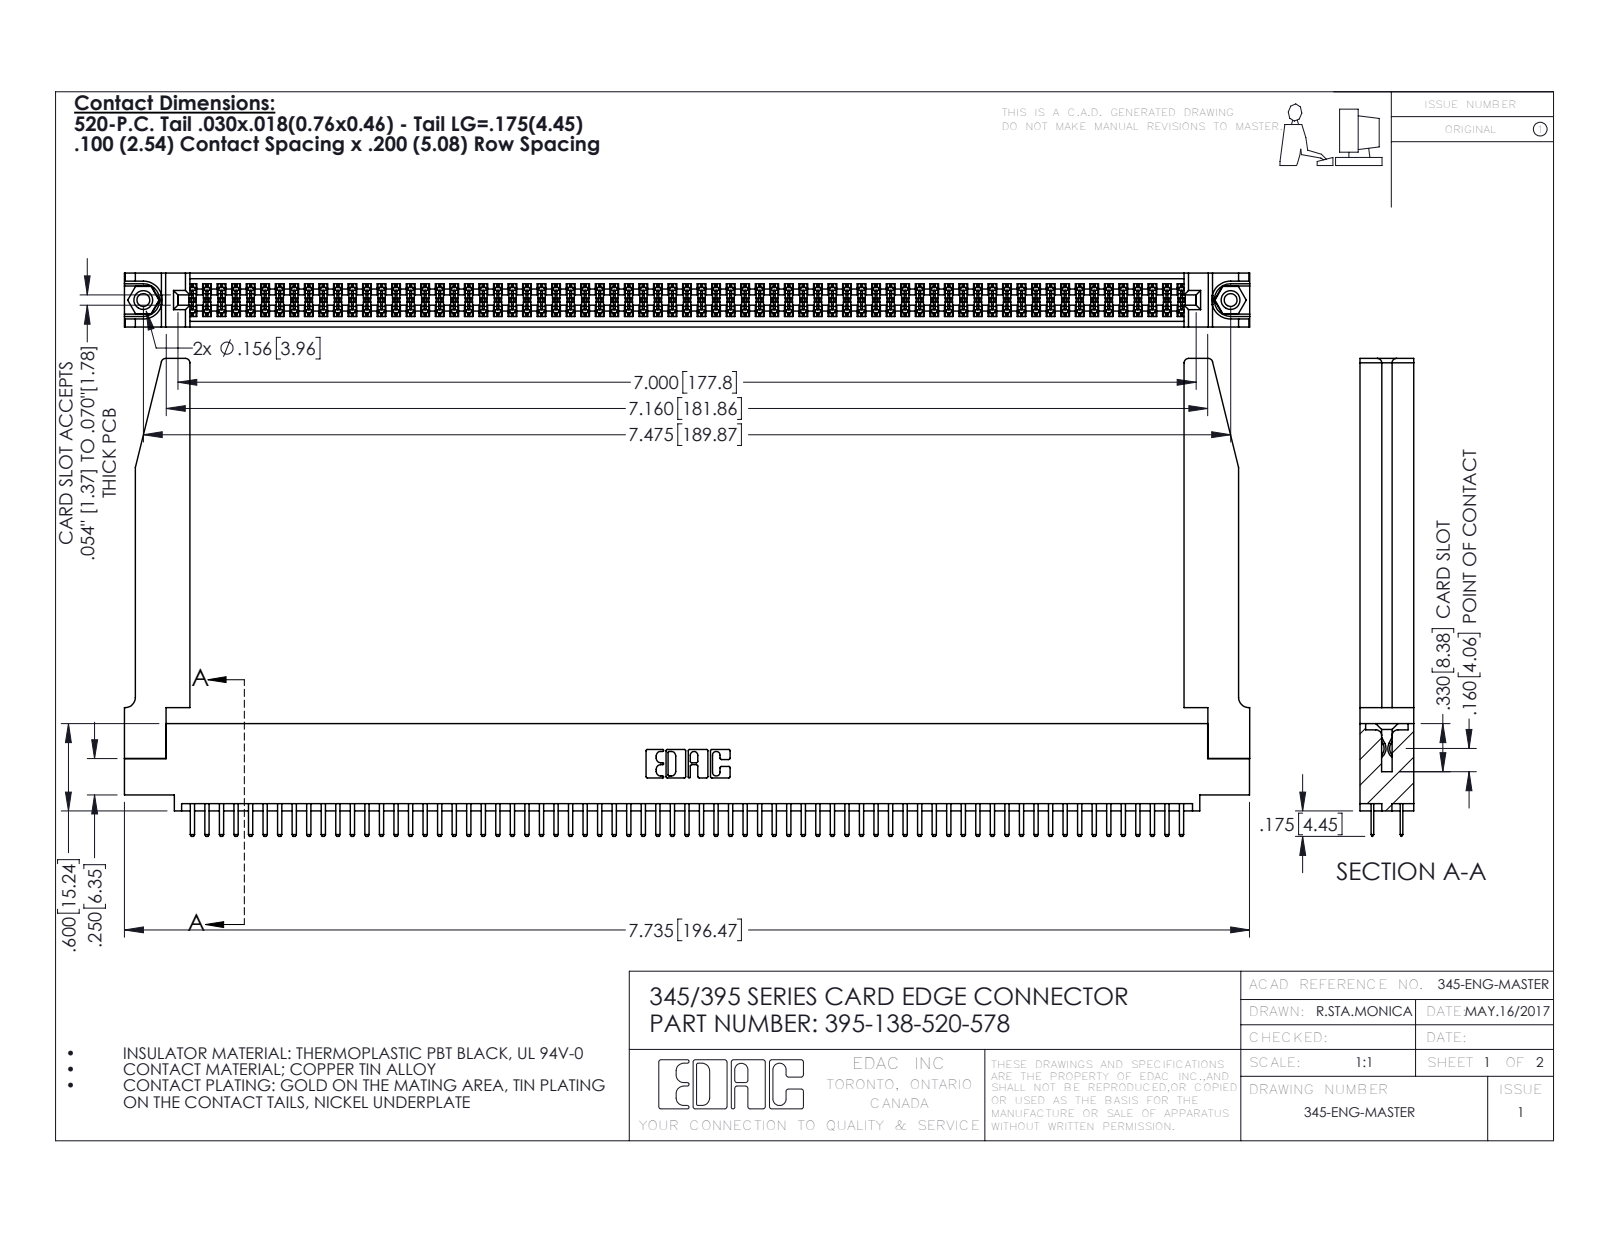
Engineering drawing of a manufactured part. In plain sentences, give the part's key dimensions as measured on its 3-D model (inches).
The part is named "345-250-001_345-250-001-102; 345-220-078_345-220-078; 345-292-001_345-293-120; 395-138-520-578 (+1 more)". Its 3-D file was written by "SolidWorks 2016 (CONFIG_CONTROL_DESIGN)". It is 143 solids with 7816 faces: 5056 planar, 2708 cylindrical and 52 other. Overall it measures 7.736 by 3.285 by 0.37 inches. Its volume is 1.646 cubic inches and its surface area 55.35 square inches. Round holes: 2 of diameter 0.089, 2 of diameter 0.125, 2 of diameter 0.156, 1 of diameter 0.064. Round bosses or shafts: 2 of diameter 0.155. Partial cylindrical surfaces (rounded edges, fillets, slot ends): 207 of radius 0.006, 142 of radius 0.01, 22 of radius 0.01, 8 of radius 0.03, 6 of radius 0.007, 6 of radius 0.031, 3 of radius 0.026, 2 of radius 0.014. The main face-to-face distances are 0.072, 0.298, 0.37, 0.2, 0.098, 0.272, 0.025, 0.225, 0.022, 0.072. The hole center spacings are 0.27, 7.239, 7.475.
